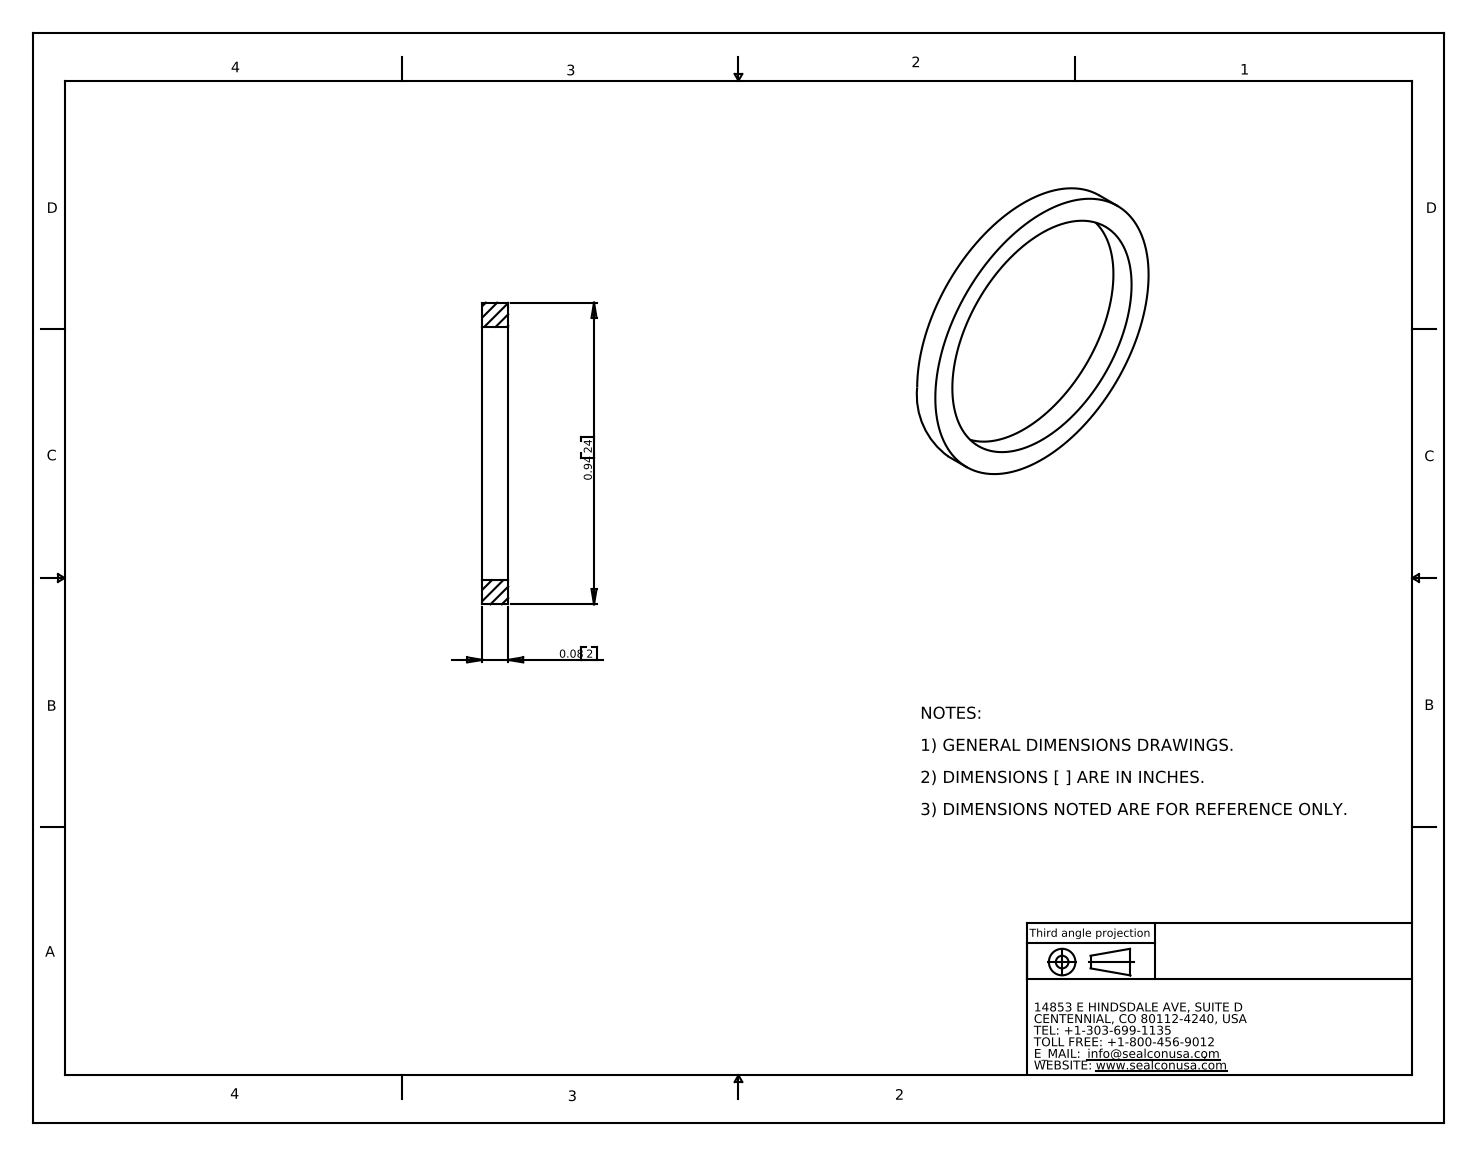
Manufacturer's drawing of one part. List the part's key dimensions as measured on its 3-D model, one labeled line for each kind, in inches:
Part name (STEP PRODUCT): SM-20-VT
STEP written by: SolidWorks 2007 (CONFIG_CONTROL_DESIGN)
Units: inches
Bodies: 1 solid, 6 faces (2 planar, 4 cylindrical, 0 other)
Overall size (bounding box): 0.94 × 0.94 × 0.08
Volume: 0.016 in³ · Surface area: 0.842 in²
Round holes (diameter × count): ⌀0.79 ×1
Round bosses / shafts (diameter × count): ⌀0.94 ×1
Main face-to-face distances: 0.08
